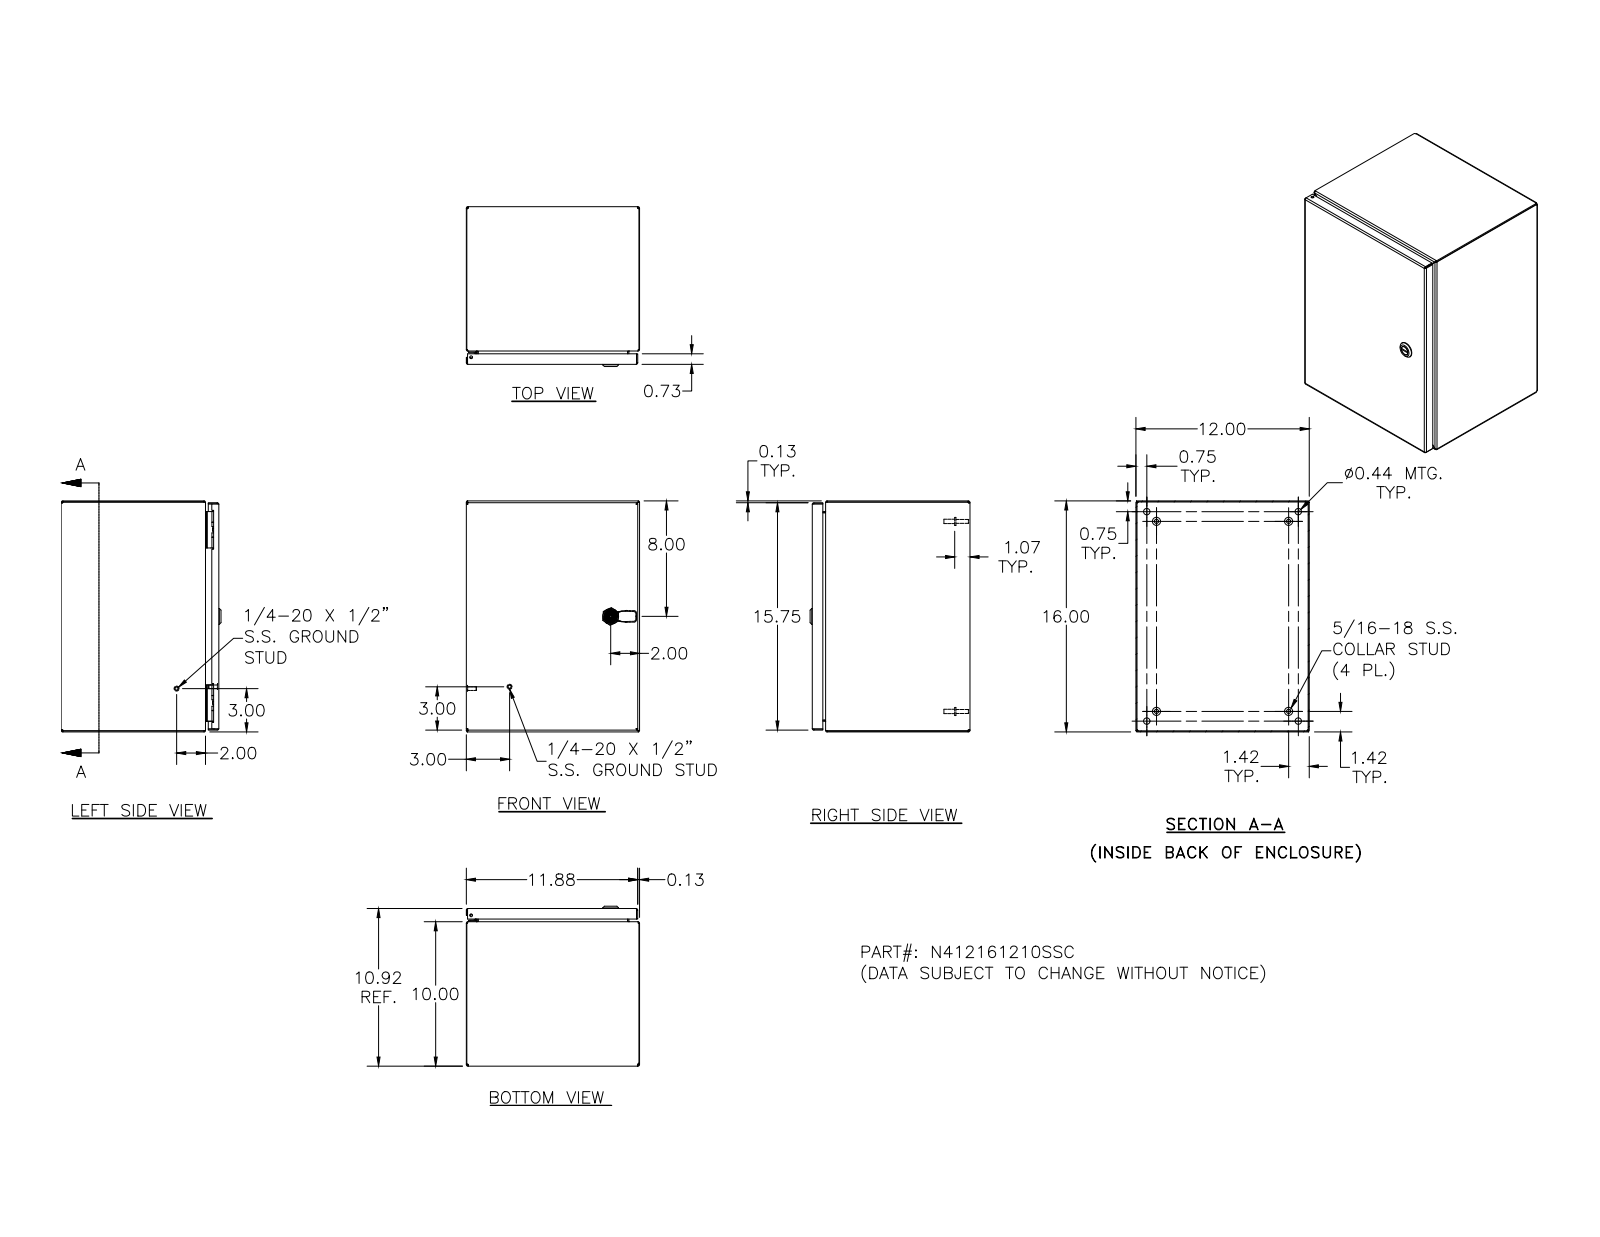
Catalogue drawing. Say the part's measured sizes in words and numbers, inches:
The part is named "N412161210SSC; N412161210SSCBKP; 388151; N4121612SSCLID (+8 more)". Its 3-D file was written by "Autodesk Inventor 2011 (AUTOMOTIVE_DESIGN)". It is 34 solids with 1384 faces: 531 planar, 509 cylindrical and 344 other. Overall it measures 16 by 12 by 11.075 inches. Its volume is 78.7 cubic inches and its surface area 2 144 square inches. Round holes: 5 of diameter 0.188, 4 of diameter 0.093, 4 of diameter 0.152, 4 of diameter 0.167, 4 of diameter 0.172, 4 of diameter 0.437, 2 of diameter 0.156, 1 of diameter 0.187, 1 of diameter 0.197, 1 of diameter 0.315, 1 of diameter 0.394, 1 of diameter 0.402. Round bosses or shafts: 10 of diameter 0.25, 4 of diameter 0.563, 4 of diameter 0.36, 4 of diameter 0.32, 4 of diameter 0.3, 4 of diameter 0.275, 4 of diameter 0.256, 4 of diameter 0.164. Partial cylindrical surfaces (rounded edges, fillets, slot ends): 30 of radius 0.031, 26 of radius 0.05, 20 of radius 0.105, 18 of radius 0.016, 14 of radius 0.125, 9 of radius 0.02, 8 of radius 0.032, 8 of radius 0.07. The main face-to-face distances are 0.074, 10.843, 11.926, 15.926, 10.769, 10.917, 12, 11.852, 16, 15.852. The hole center spacings are 12, 0.017, 0.66, 0.019, 0.5, 0.648, 0.652, 0.656.
